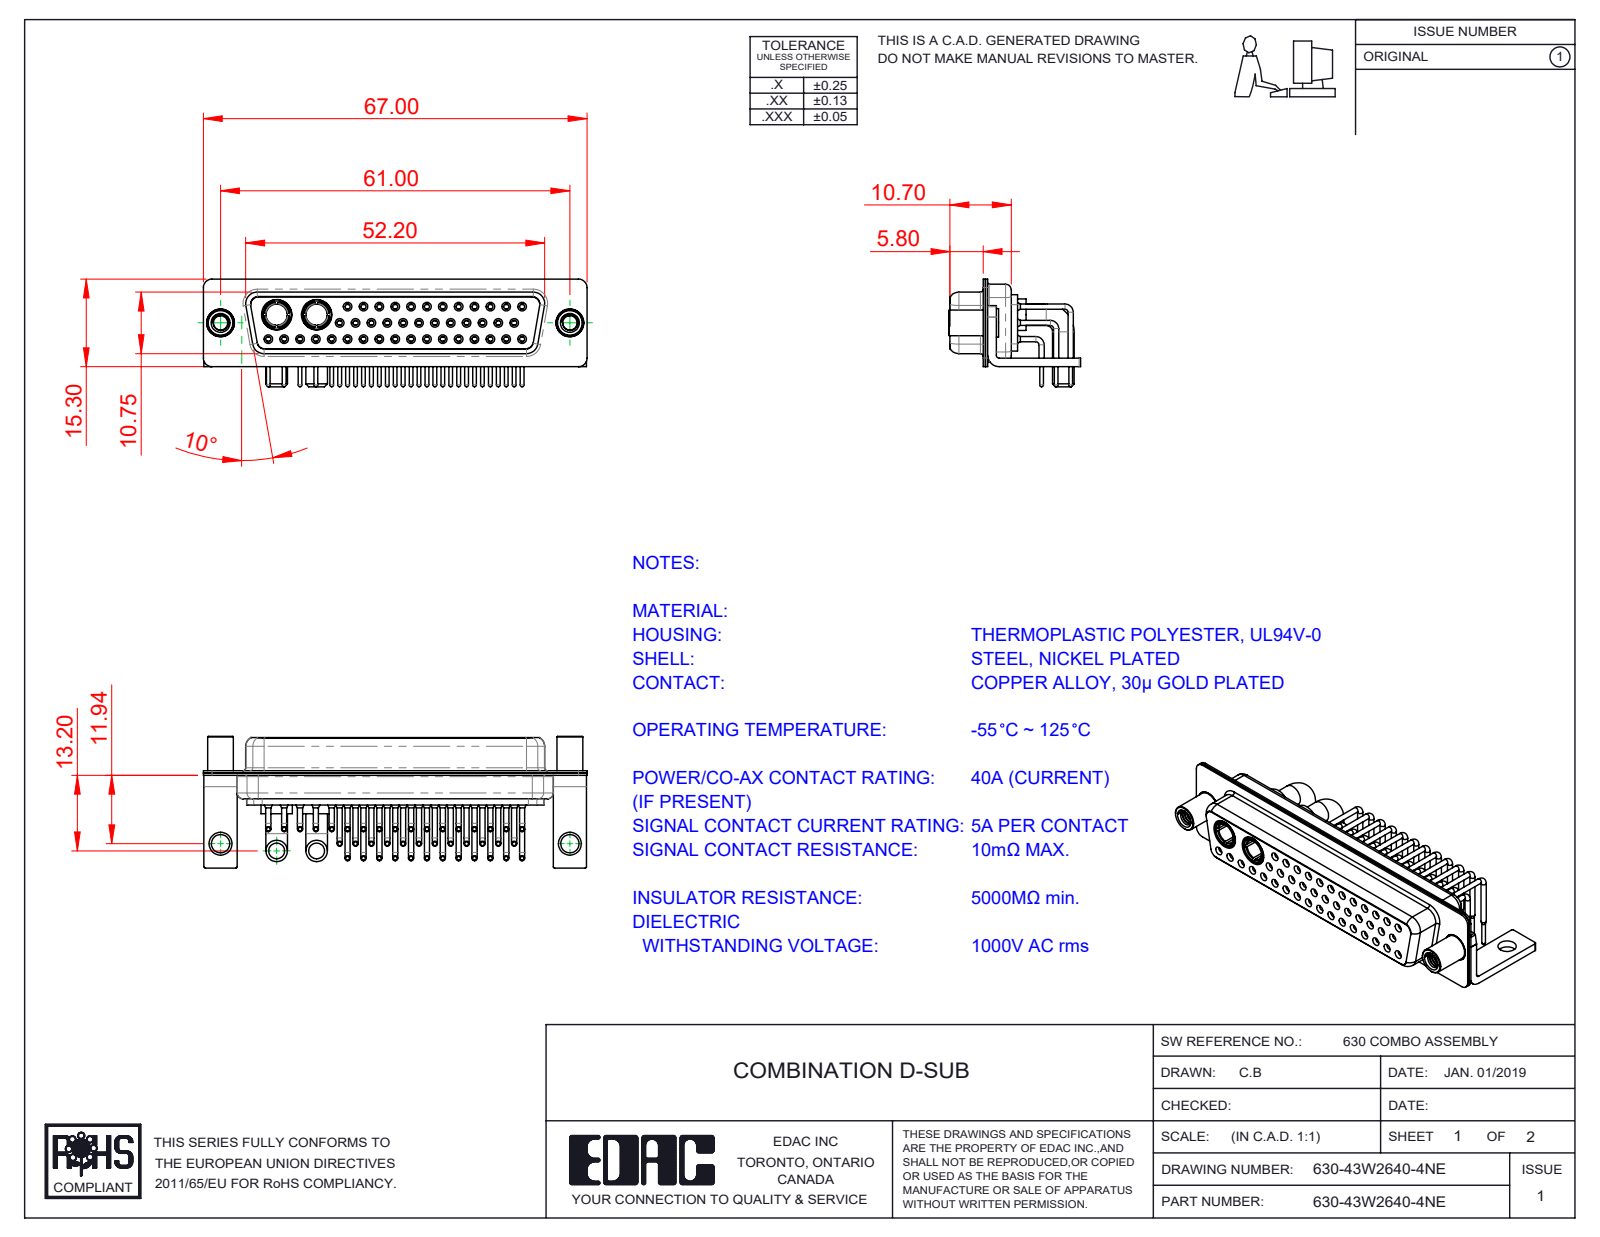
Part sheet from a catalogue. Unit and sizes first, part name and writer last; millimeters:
Units: millimetres
Overall size (bounding box): 67 × 23 × 18.8
Round holes (diameter × count): ⌀0.9 ×41, ⌀1.1 ×41, ⌀1.5 ×41, ⌀2 ×41, ⌀1.6 ×29, ⌀1.7 ×12, ⌀4.85 ×4, ⌀2.5 ×2, ⌀3.2 ×2, ⌀3.7 ×2, ⌀4 ×2, ⌀4.05 ×2
Round bosses / shafts (diameter × count): ⌀0.9 ×41, ⌀0.65 ×41, ⌀1.6 ×12, ⌀3.75 ×4, ⌀5.5 ×2, ⌀5.2 ×2, ⌀5 ×2, ⌀4.96 ×2
Partial cylindrical surfaces — rounded edges, fillets, slot ends (radius × count): R0.25 ×16, R1.5 ×16, R2 ×13, R1.35 ×12, R1.6 ×8, R0.5 ×5, R0.6 ×4, R0.65 ×4
Main face-to-face distances: 0.4, 6, 1.5, 5.6, 0.8, 5.8, 5.2, 11.28, 1.82, 6.2
Hole centre spacings: 2.77, 3.16, 5.54, 8.31, 11.08, 13.85, 16.62, 19.39
Volume: 7 857 mm³ · Surface area: 17 007 mm²
Bodies: 52 solids, 2706 faces (762 planar, 1202 cylindrical, 742 other)
Part name (STEP PRODUCT): 630Combo Shell Front_50 Contacts; 630Combo Housing_43W2; 630Combo Contact Row 3; 630Combo Threaded Standoff_D (+6 more)
STEP written by: SolidWorks 2020 (CONFIG_CONTROL_DESIGN)
